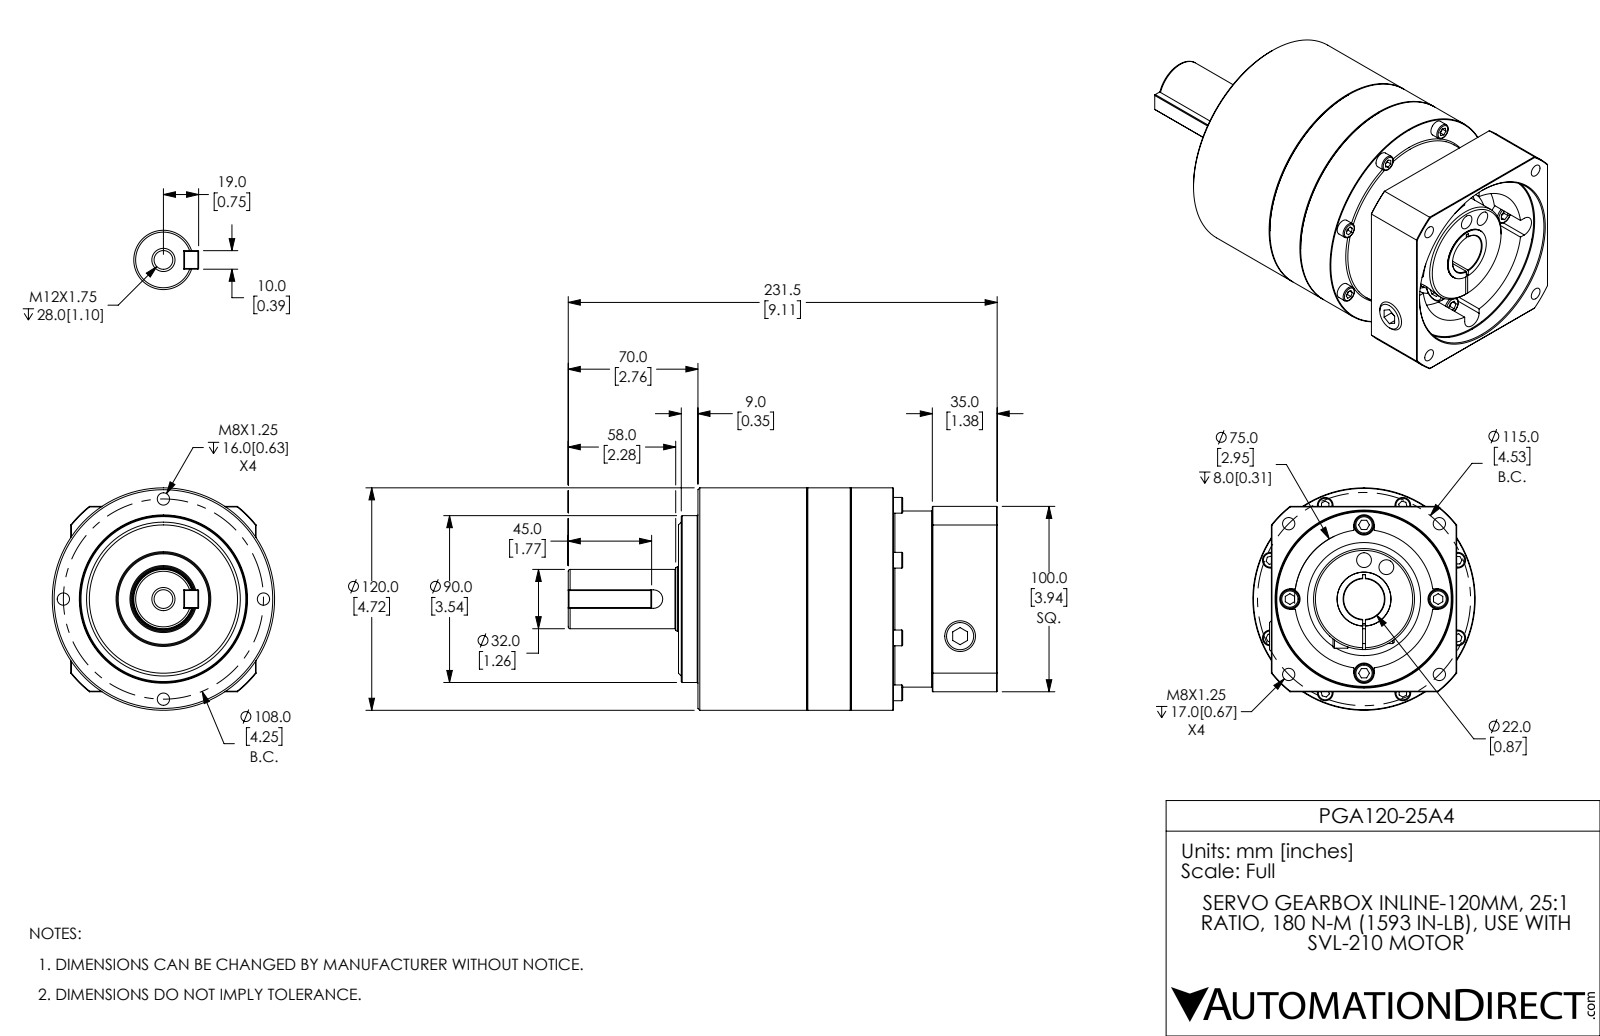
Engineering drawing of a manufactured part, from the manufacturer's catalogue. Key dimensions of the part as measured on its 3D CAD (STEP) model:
Part name (STEP PRODUCT): PGA120-25A4
STEP written by: SolidWorks 2019 (CONFIG_CONTROL_DESIGN)
Units: millimetres
Bodies: 1 solid, 431 faces (184 planar, 105 cylindrical, 142 other)
Overall size (bounding box): 231.5 × 120 × 120
Volume: 1 645 000 mm³ · Surface area: 125 909 mm²
Round holes (diameter × count): ⌀6.65 ×8, ⌀11 ×4, ⌀8 ×2, ⌀8.8 ×1, ⌀10.11 ×1, ⌀14.25 ×1, ⌀22 ×1, ⌀61 ×1, ⌀75 ×1, ⌀95 ×1
Round bosses / shafts (diameter × count): ⌀8.5 ×8, ⌀10 ×4, ⌀120 ×1, ⌀90 ×1, ⌀54.5 ×1, ⌀35 ×1, ⌀32 ×1, ⌀29 ×1
Partial cylindrical surfaces — rounded edges, fillets, slot ends (radius × count): R3.32 ×1, R5 ×1, R7 ×1, R64 ×1
Main face-to-face distances: 100, 28, 10.5, 105.5, 116, 21, 126.5, 137, 7, 8
Hole centre spacings: 40.67, 42.79, 67.2, 90.33, 103.02, 14, 40, 54
